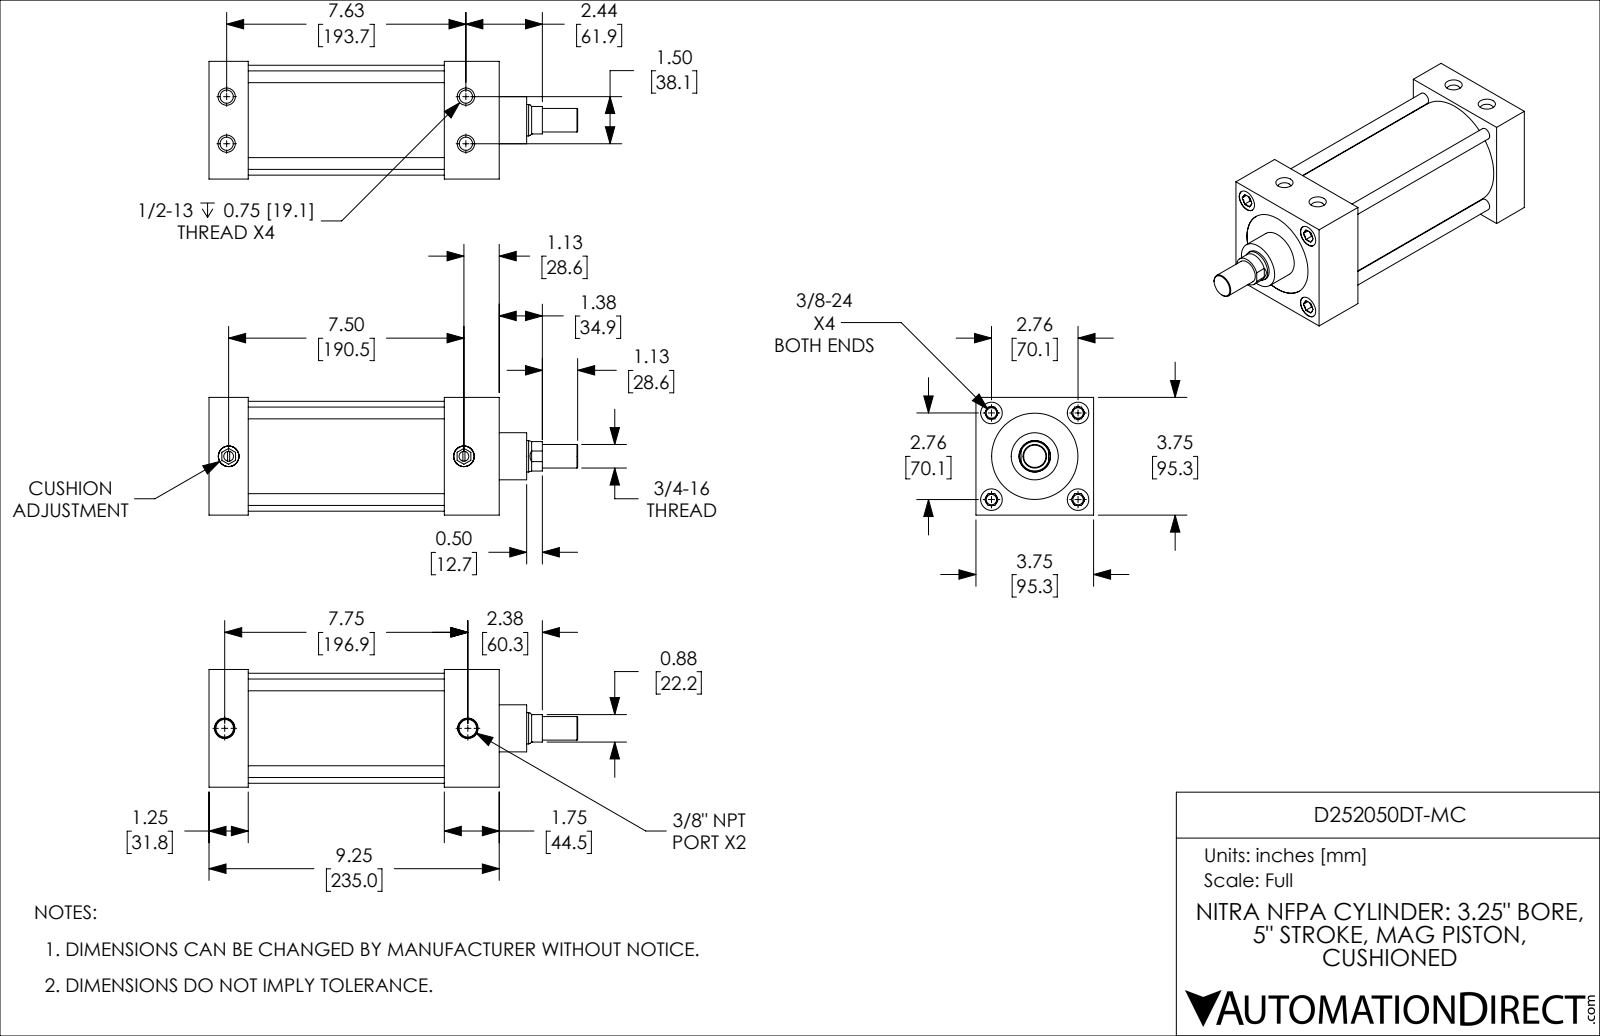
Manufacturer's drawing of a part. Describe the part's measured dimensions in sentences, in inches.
The part is named "D252050DT-MC; D252050DT-MC_CUSHION; D252050DT-MC_BODY; D252050DT-MC_PISTON_KK1". Its 3-D file was written by "SolidWorks 2019 (CONFIG_CONTROL_DESIGN)". It is 4 solids with 246 faces: 90 planar, 78 cylindrical and 78 other. Overall it measures 11.75 by 3.75 by 3.75 inches. Its volume is 67.57 cubic inches and its surface area 351.1 square inches. Round holes: 4 of diameter 0.332, 4 of diameter 0.422, 4 of diameter 0.687, 2 of diameter 0.312, 2 of diameter 0.562, 2 of diameter 0.656, 1 of diameter 1.001, 1 of diameter 2.75, 1 of diameter 3.251. Round bosses or shafts: 4 of diameter 0.375, 2 of diameter 0.657, 1 of diameter 3.501, 1 of diameter 3.249, 1 of diameter 1.5, 1 of diameter 0.999, 1 of diameter 0.75. Partial cylindrical surfaces (rounded edges, fillets, slot ends): 1 of radius 0.469. The main face-to-face distances are 1.25, 3.75, 7.5, 6.25, 2.5, 5, 9.25, 8, 6.75, 1.75. The hole center spacings are 0.753, 1.952, 2.76, 7.724, 1.5, 3.903, 7.625, 7.771.
